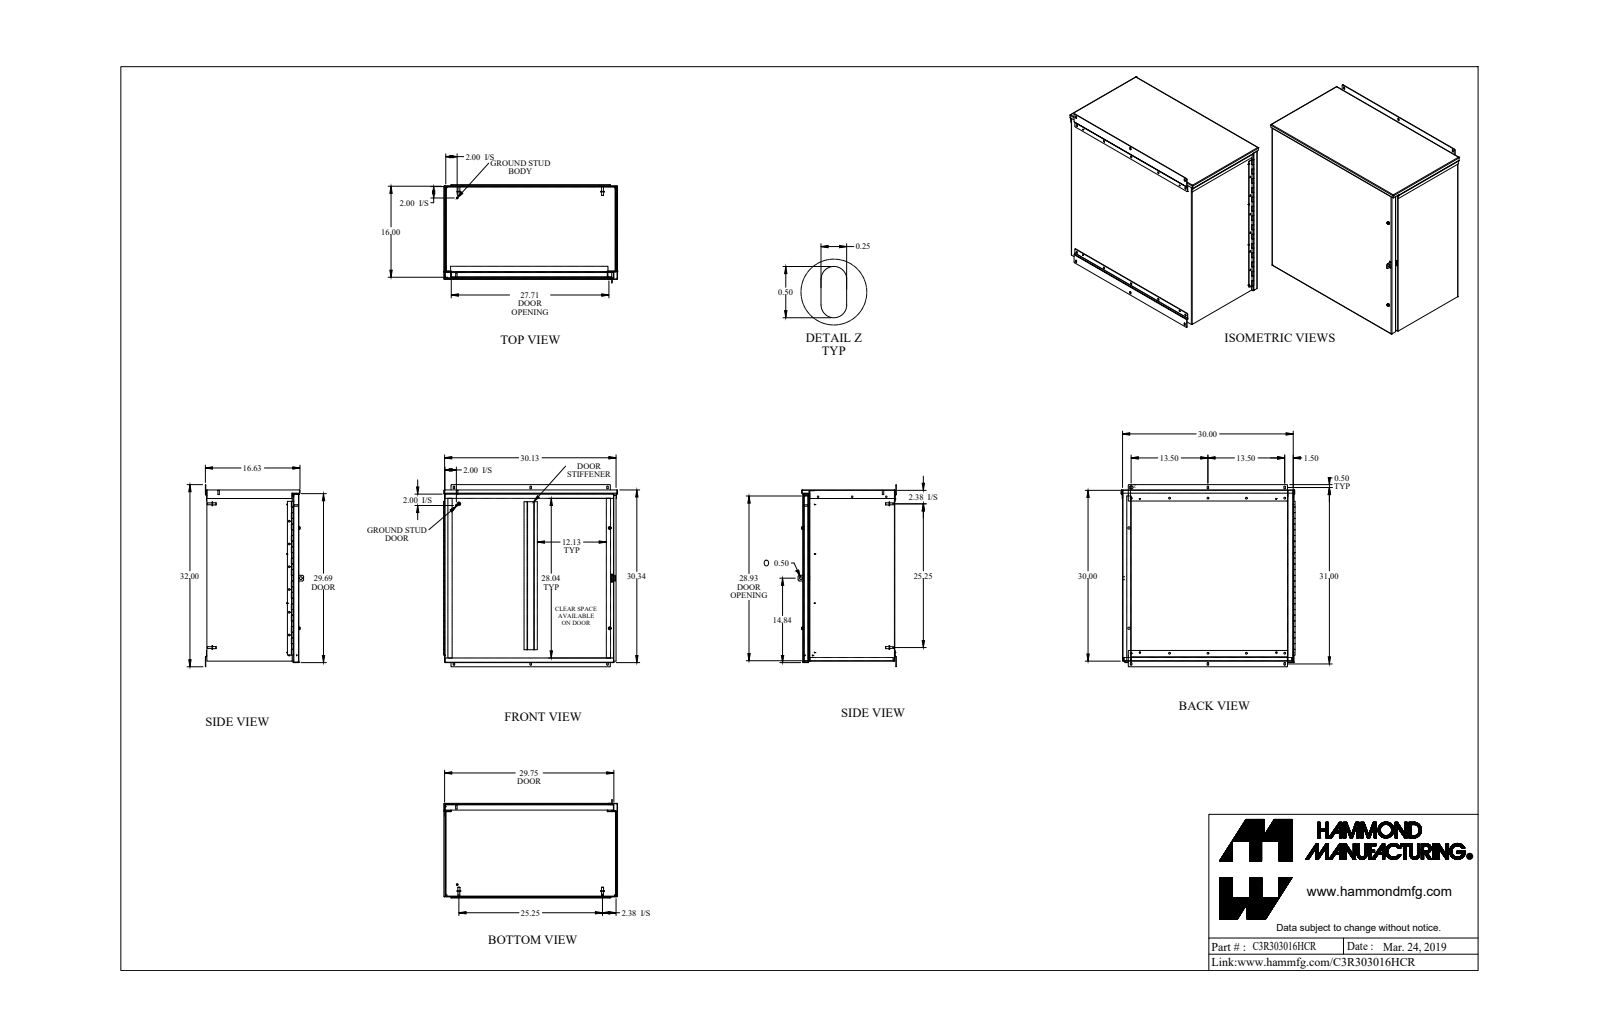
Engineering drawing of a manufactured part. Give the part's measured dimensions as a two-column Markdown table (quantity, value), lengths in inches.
| quantity | value |
| --- | --- |
| part name | C3R303016HCR_Default |
| STEP written by | SolidWorks 2019 (CONFIG_CONTROL_DESIGN) |
| units | inches |
| bodies | 35 solids, 1014 faces (549 planar, 411 cylindrical, 54 other) |
| overall size | 32 × 30.571 × 17.26 |
| volume | 340.9 in³ |
| surface area | 9 314 in² |
| round holes (diameter × count) | 0.312 × 10, 0.304 × 6, 0.137 × 4, 0.14 × 4, 0.25 × 3, 0.26 × 3, 0.313 × 3, 0.266 × 2, 0.28 × 2, 0.29 × 2, 0.397 × 2, 0.188 × 1 |
| round bosses / shafts (diameter × count) | 0.131 × 10, 0.65 × 4, 0.375 × 4, 0.33 × 4, 0.51 × 3, 0.244 × 3, 0.187 × 3, 0.5 × 2 |
| partial cylindrical surfaces (radius × count) | 0.036 × 39, 0.108 × 39, 0.125 × 23, 0.171 × 3, 0.25 × 2 |
| main face-to-face distances | 0.072, 16.1, 30, 29.928, 16.172, 16.028, 29.856, 30.072, 0.259, 0.187 |
| hole center spacings | 6.75, 28.074, 13.5, 30.411, 4, 27.25, 1.505, 5.252 |
